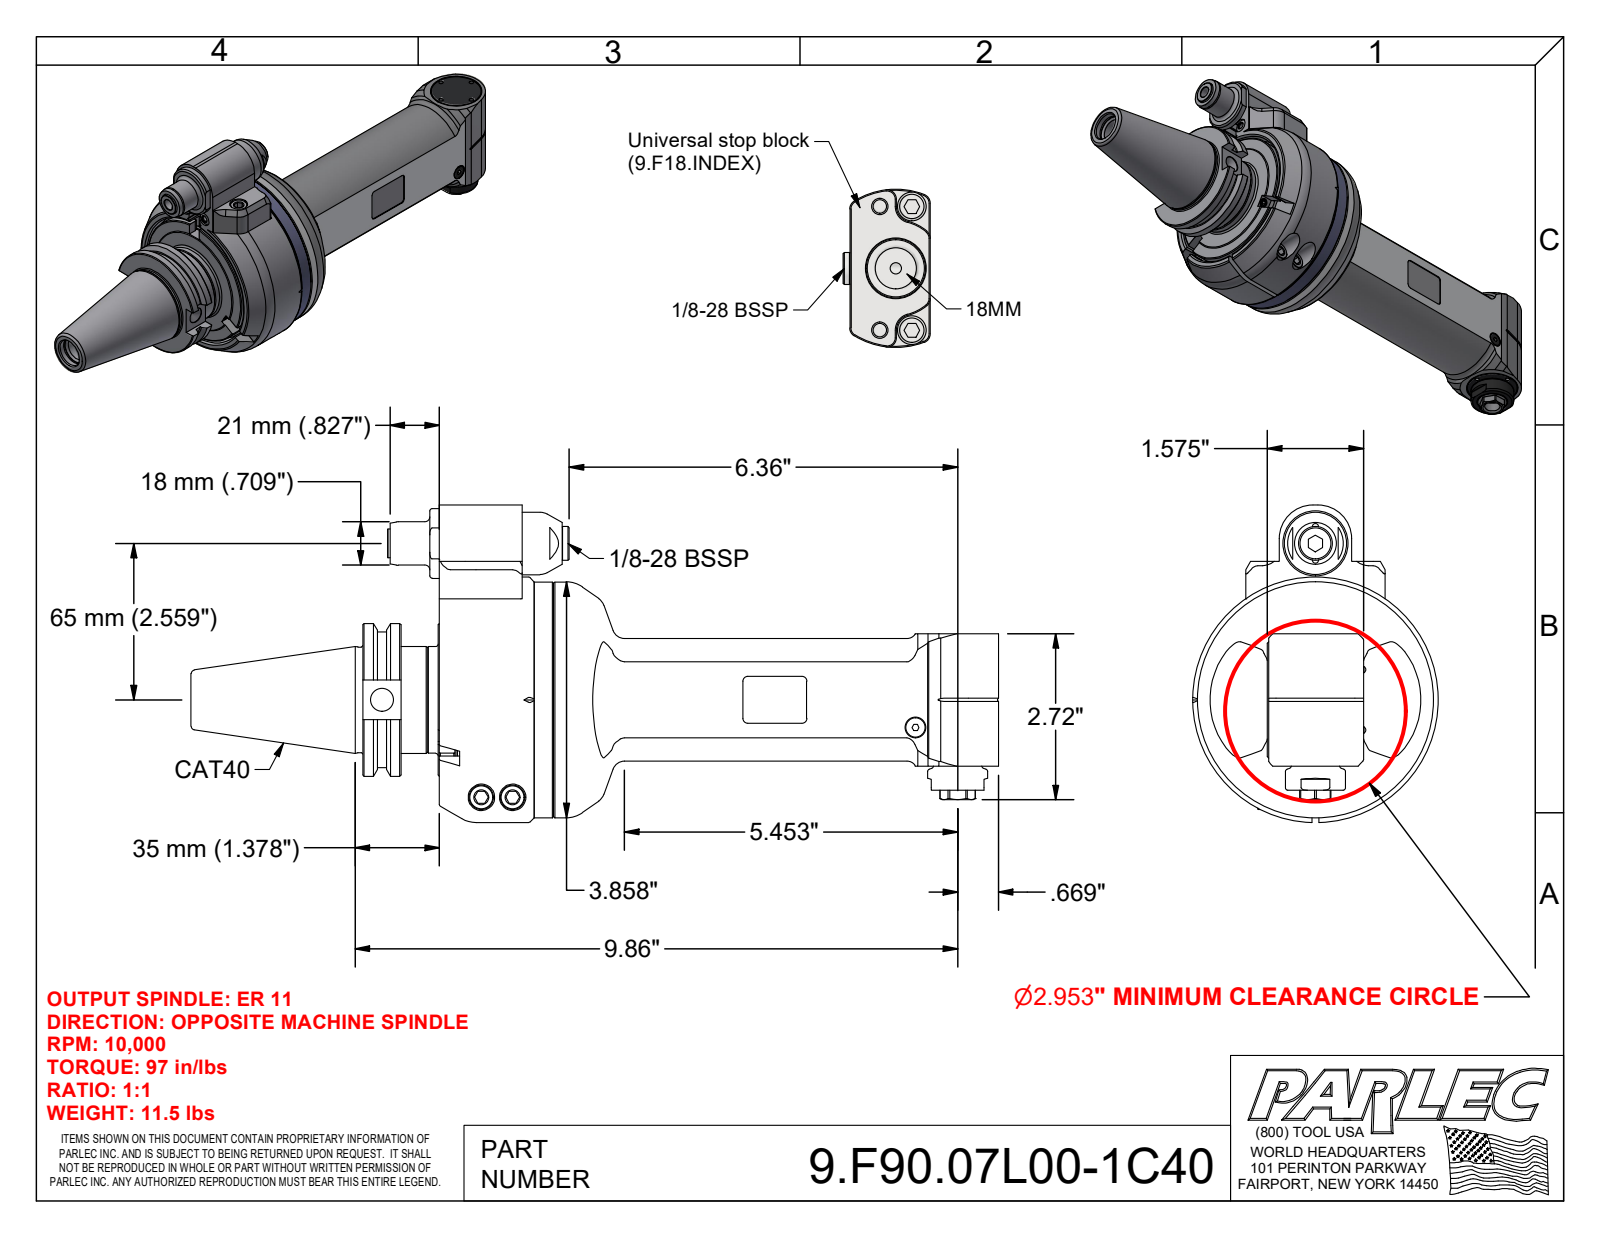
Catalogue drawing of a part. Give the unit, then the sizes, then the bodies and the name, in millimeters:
Units: millimetres
Overall size (bounding box): 335.8 × 132 × 102
Round holes (diameter × count): ⌀2.6 ×6, ⌀3.2 ×4, ⌀5 ×3, ⌀6.5 ×3, ⌀3.3 ×2, ⌀4.2 ×2, ⌀8 ×2, ⌀10.4 ×2, ⌀11 ×2, ⌀12.5 ×2, ⌀2.5 ×1, ⌀3 ×1
Round bosses / shafts (diameter × count): ⌀10 ×4, ⌀18 ×3, ⌀12 ×2, ⌀8 ×2, ⌀6 ×2, ⌀2.5 ×2, ⌀102 ×1, ⌀98 ×1
Partial cylindrical surfaces — rounded edges, fillets, slot ends (radius × count): R1 ×14, R2 ×12, R3 ×6, R4 ×4, R0.4 ×2, R0.5 ×2, R8 ×2, R14 ×2
Main face-to-face distances: 0.5, 40, 1, 7, 7.5, 32, 8.5, 39.5, 32.5, 9
Hole centre spacings: 12.5, 8.3, 11.7, 17.7, 7, 12.8, 16.5, 18.8
Volume: 969 000 mm³ · Surface area: 139 800 mm²
Bodies: 4 solids, 624 faces (275 planar, 167 cylindrical, 182 other)
Part name (STEP PRODUCT): 9.F90.07L00-1C40; 9.F90.07L00; 9_GA1_446_2 (EVO, Type 1, C40, 65mm, 35mm)
STEP written by: Autodesk Inventor 2022 (AUTOMOTIVE_DESIGN)
